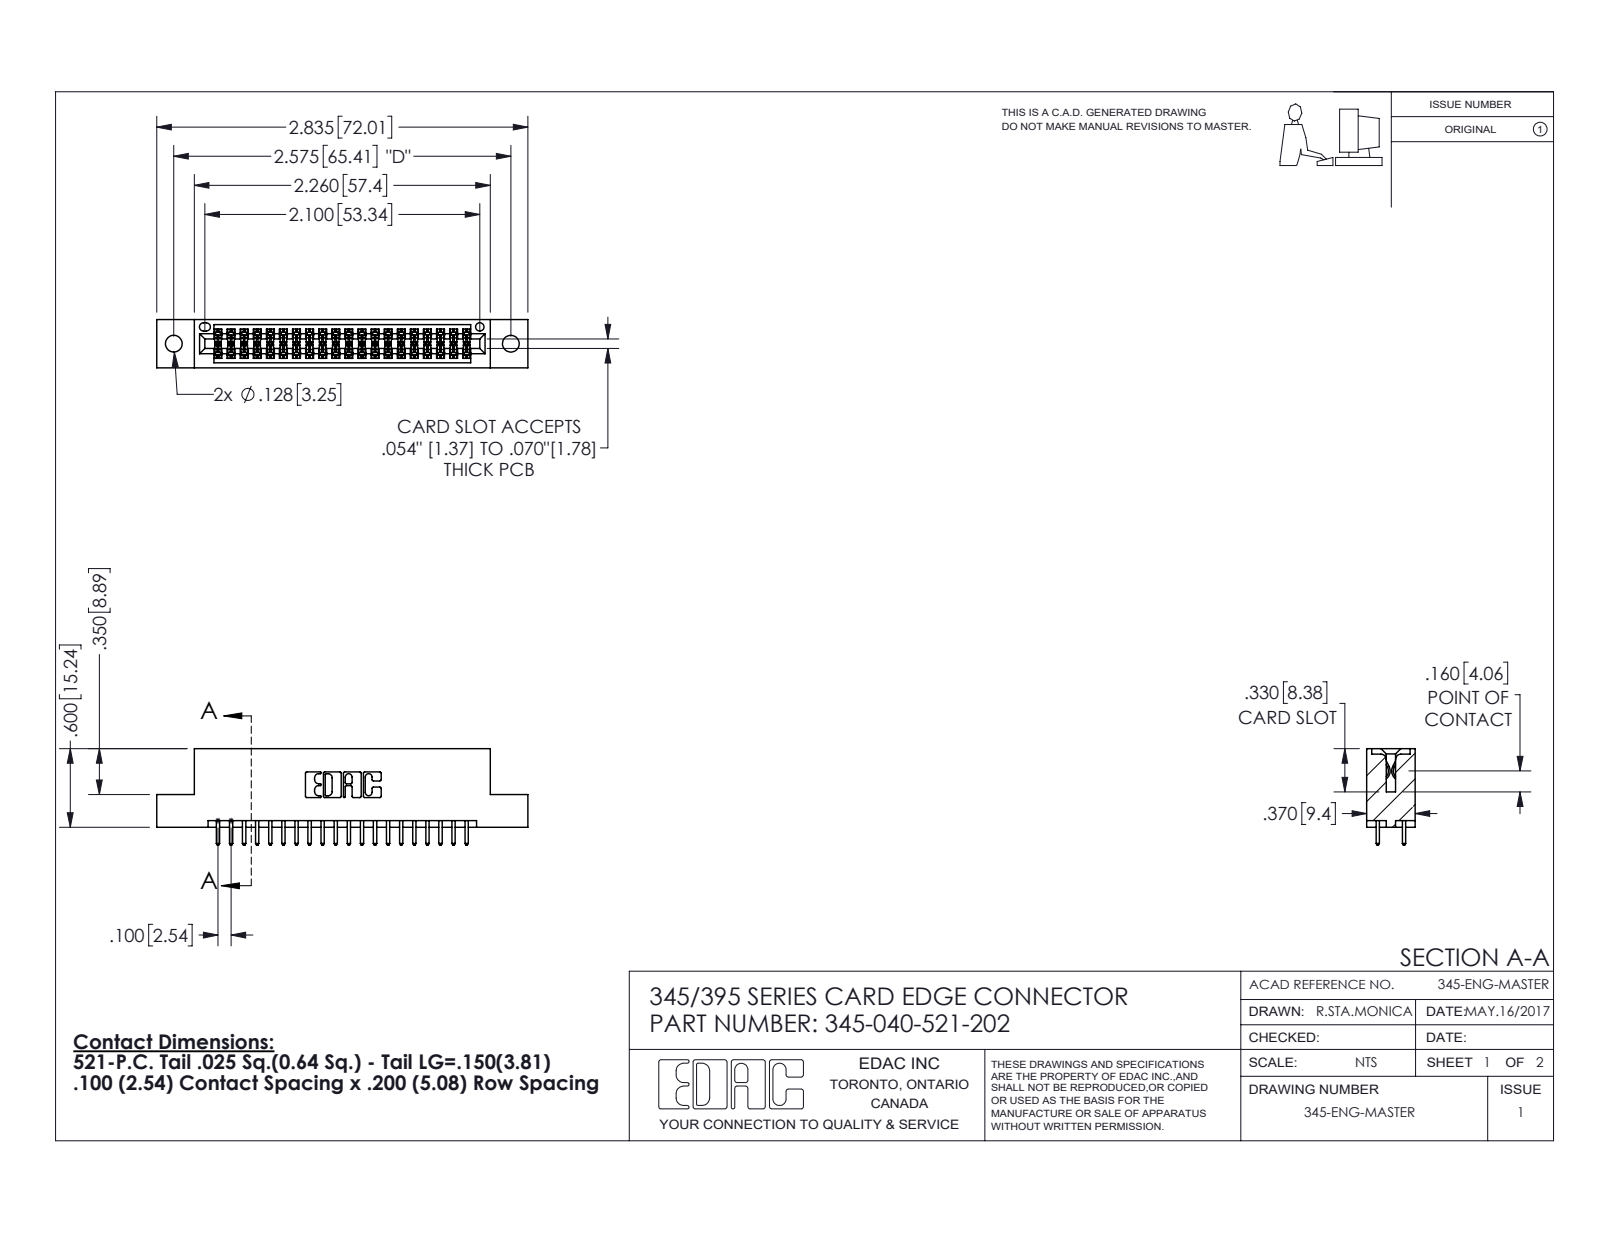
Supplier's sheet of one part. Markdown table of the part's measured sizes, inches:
| quantity | value |
| --- | --- |
| part name | 345-040-521-202; 345 Part_Flush Mounting Lugs - 0.128 Dia; 345-292-001_345-293-121 |
| STEP written by | SolidWorks 2016 (CONFIG_CONTROL_DESIGN) |
| units | inches |
| bodies | 41 solids, 2126 faces (1400 planar, 726 cylindrical, 0 other) |
| overall size | 2.835 × 0.737 × 0.37 |
| volume | 0.411 in³ |
| surface area | 14.19 in² |
| round holes (diameter × count) | 0.128 × 2, 0.064 × 1 |
| partial cylindrical surfaces (radius × count) | 0.006 × 60, 0.01 × 40, 0.01 × 22, 0.007 × 6, 0.031 × 6, 0.026 × 3, 0.014 × 2, 0.019 × 2 |
| main face-to-face distances | 0.298, 0.072, 0.2, 0.37, 0.098, 0.272, 0.025, 0.225, 0.175, 0.149 |
| hole center spacings | 0.27, 2.341, 2.575 |
